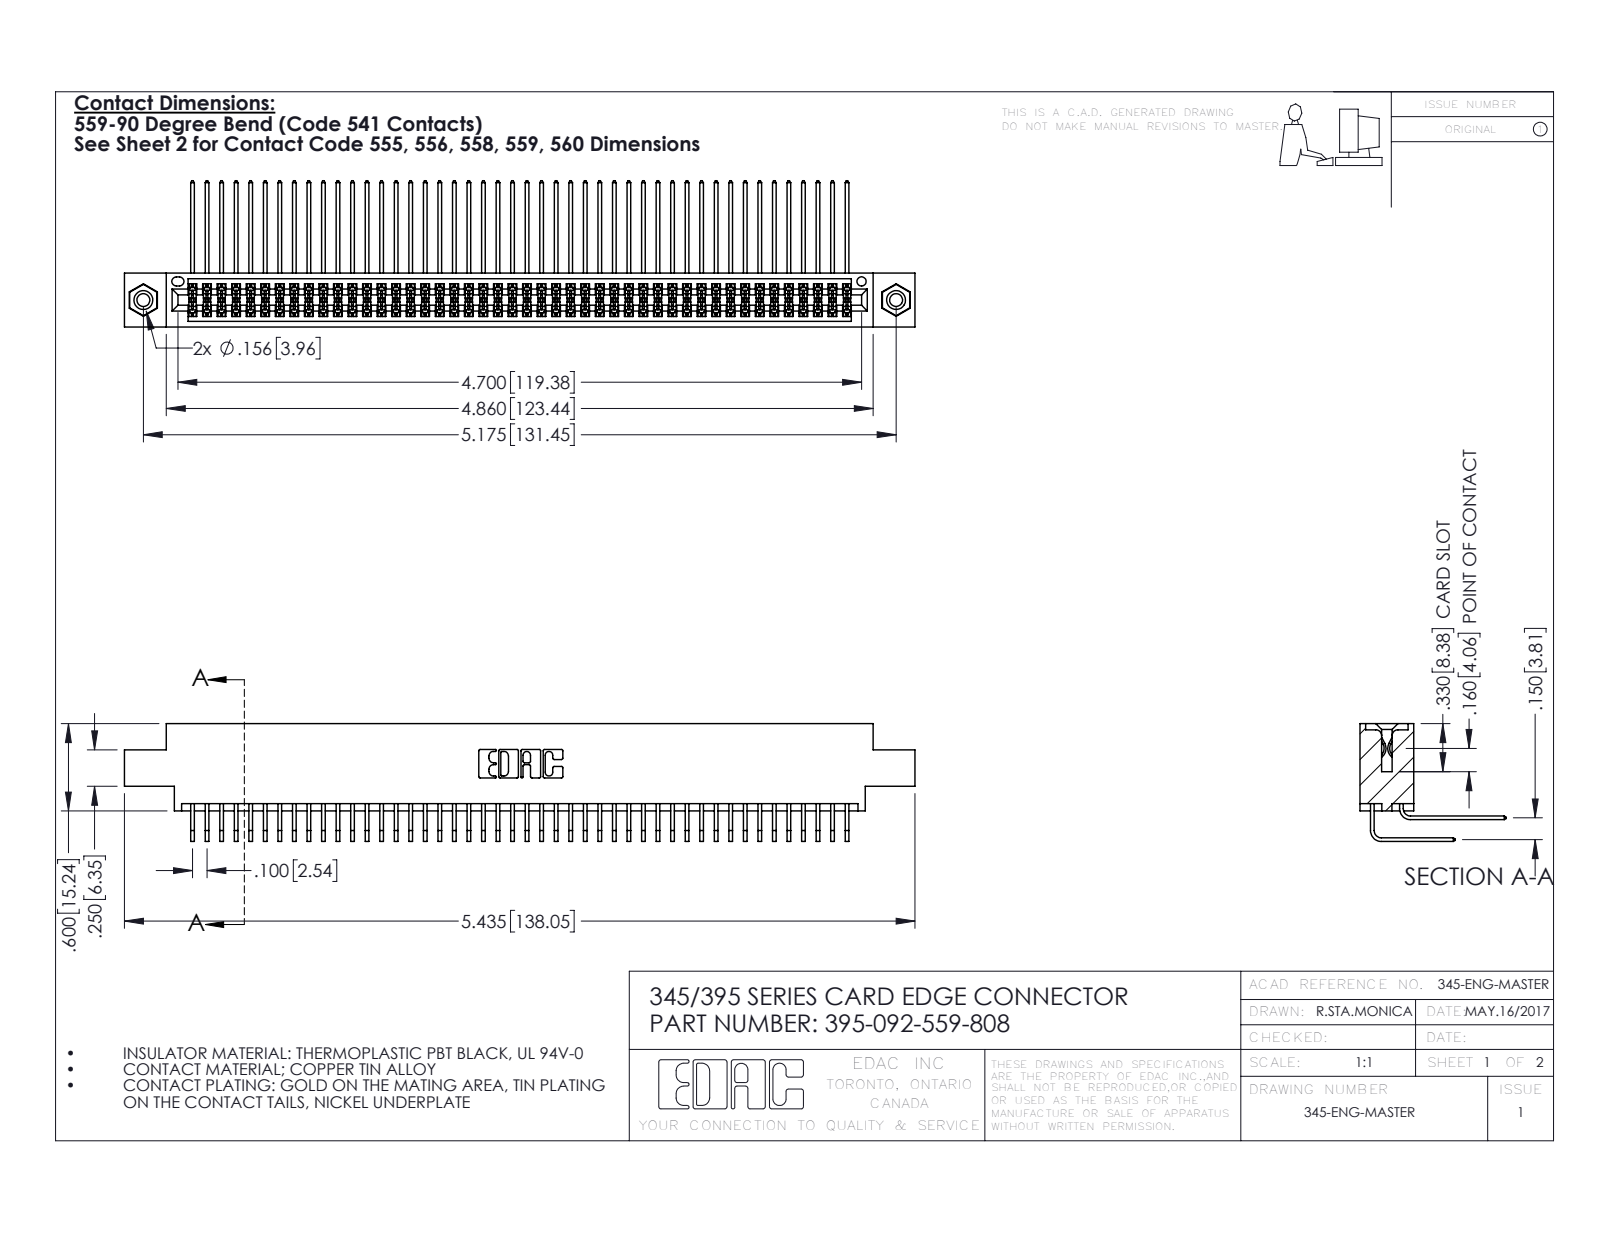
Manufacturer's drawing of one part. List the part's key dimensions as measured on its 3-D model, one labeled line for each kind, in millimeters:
Part name (STEP PRODUCT): 345-250-001_345-250-003-102; 345-292-001_559 Tail - 2; 345 Part_0.170 Offset - 0.156 Dia-TI; 345-292-001_558 559 Tail - 1 (+1 more)
STEP written by: SolidWorks 2016 (CONFIG_CONTROL_DESIGN)
Units: millimetres
Bodies: 95 solids, 4974 faces (3336 planar, 1622 cylindrical, 16 other)
Overall size (bounding box): 138 × 25.5 × 20.5
Volume: 13 900 mm³ · Surface area: 23 210 mm²
Round holes (diameter × count): ⌀2.3 ×2, ⌀3.2 ×2, ⌀4 ×2, ⌀1.6 ×1
Round bosses / shafts (diameter × count): ⌀3.9 ×2
Partial cylindrical surfaces — rounded edges, fillets, slot ends (radius × count): R0.2 ×138, R0.3 ×22, R0.2 ×6, R0.8 ×6, R0.7 ×3, R0.4 ×2, R0.5 ×2, R0.6 ×2
Main face-to-face distances: 1.8, 7.6, 9.4, 5.1, 2.5, 6.9, 0.6, 5.7, 4.4, 3.8
Hole centre spacings: 6.9, 125.5, 131.4
